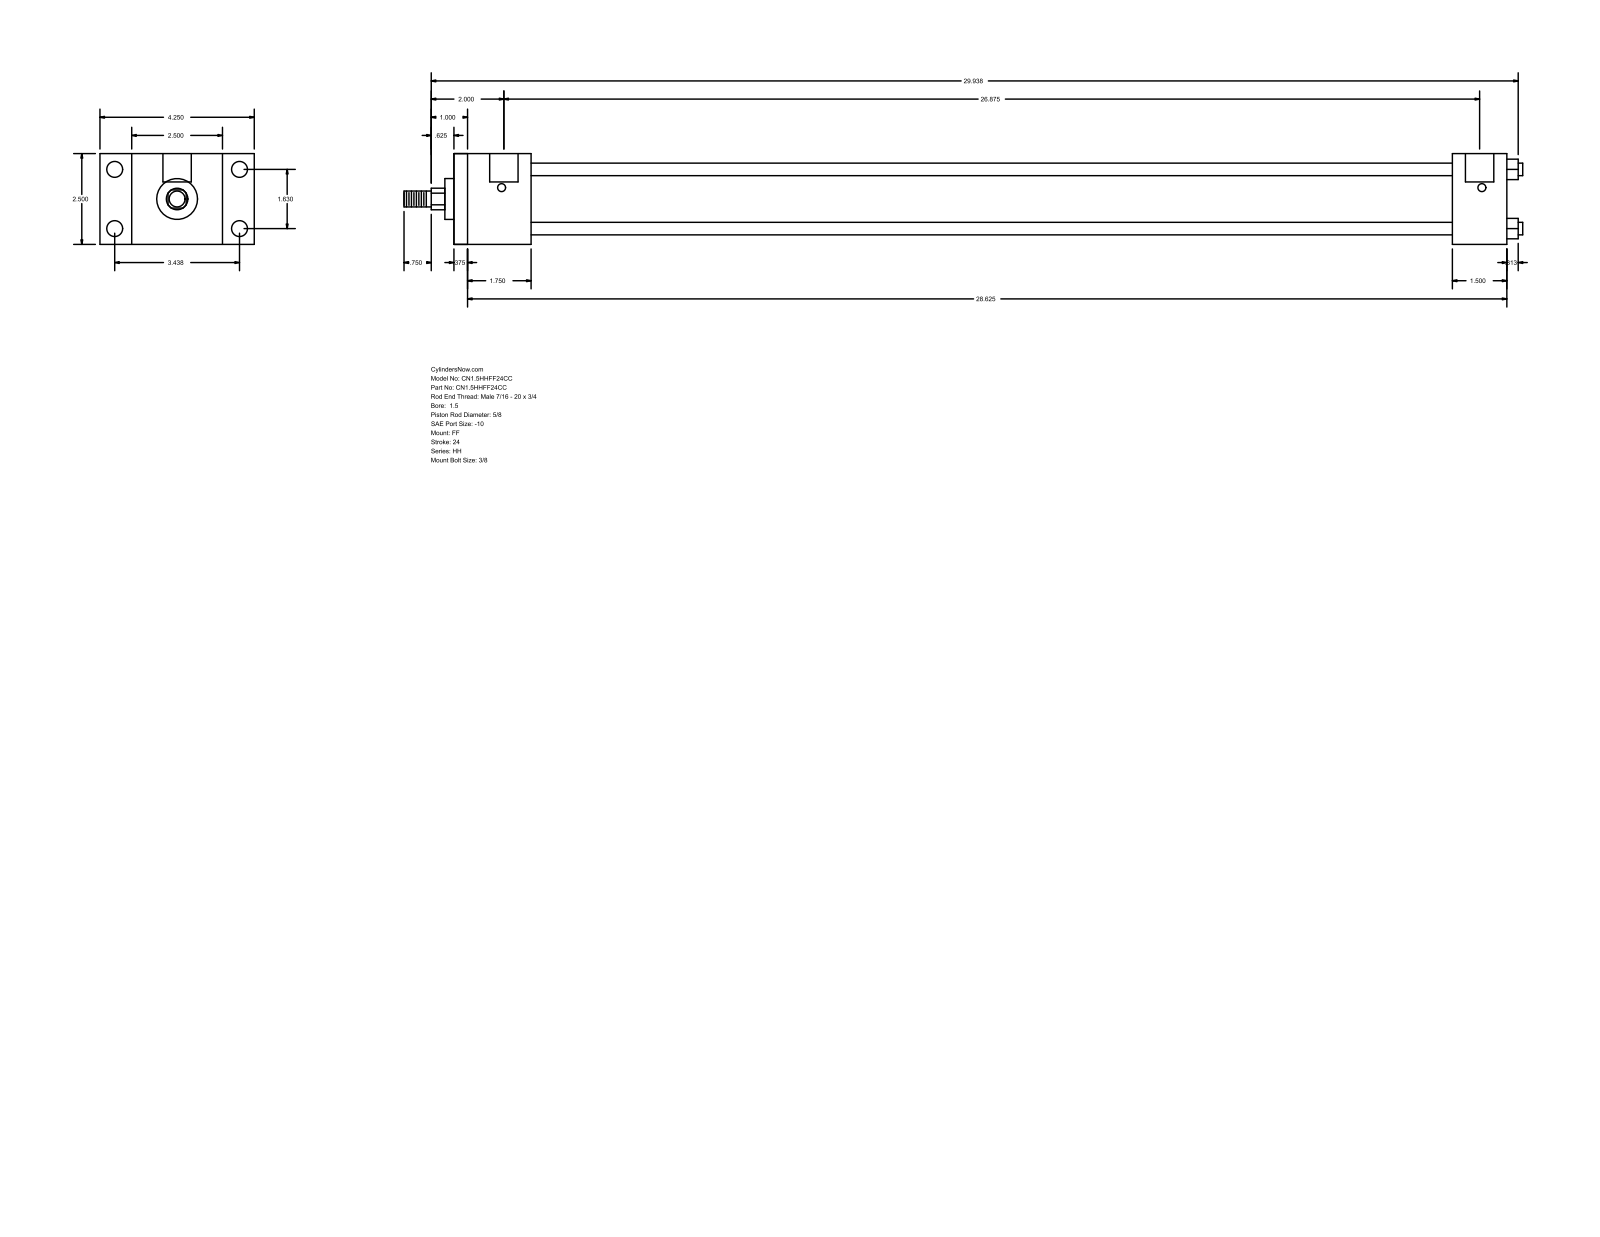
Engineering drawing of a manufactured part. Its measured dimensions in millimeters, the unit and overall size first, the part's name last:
Units: millimetres
Overall size (bounding box): 782.64 × 107.95 × 63.5
Round holes (diameter × count): ⌀5.56 ×4, ⌀11.13 ×4, ⌀19.84 ×2
Round bosses / shafts (diameter × count): ⌀8.76 ×4, ⌀44.45 ×1, ⌀28.57 ×1, ⌀15.88 ×1, ⌀11.11 ×1
Partial cylindrical surfaces — rounded edges, fillets, slot ends (radius × count): R7.54 ×1
Main face-to-face distances: 63.5, 736.6, 38.1, 9.52, 727.08, 44.45, 53.97, 682.63, 698.5, 688.98
Hole centre spacings: 1.59, 41.4, 87.32, 96.64, 684.21, 685.8, 682.62
Bodies: 0 solids, 92 faces (64 planar, 28 cylindrical, 0 other)
Part name (STEP PRODUCT): HH_FF__0150_0.625
STEP written by: GSSL Pune (CONFIG_CONTROL_DESIGN)
